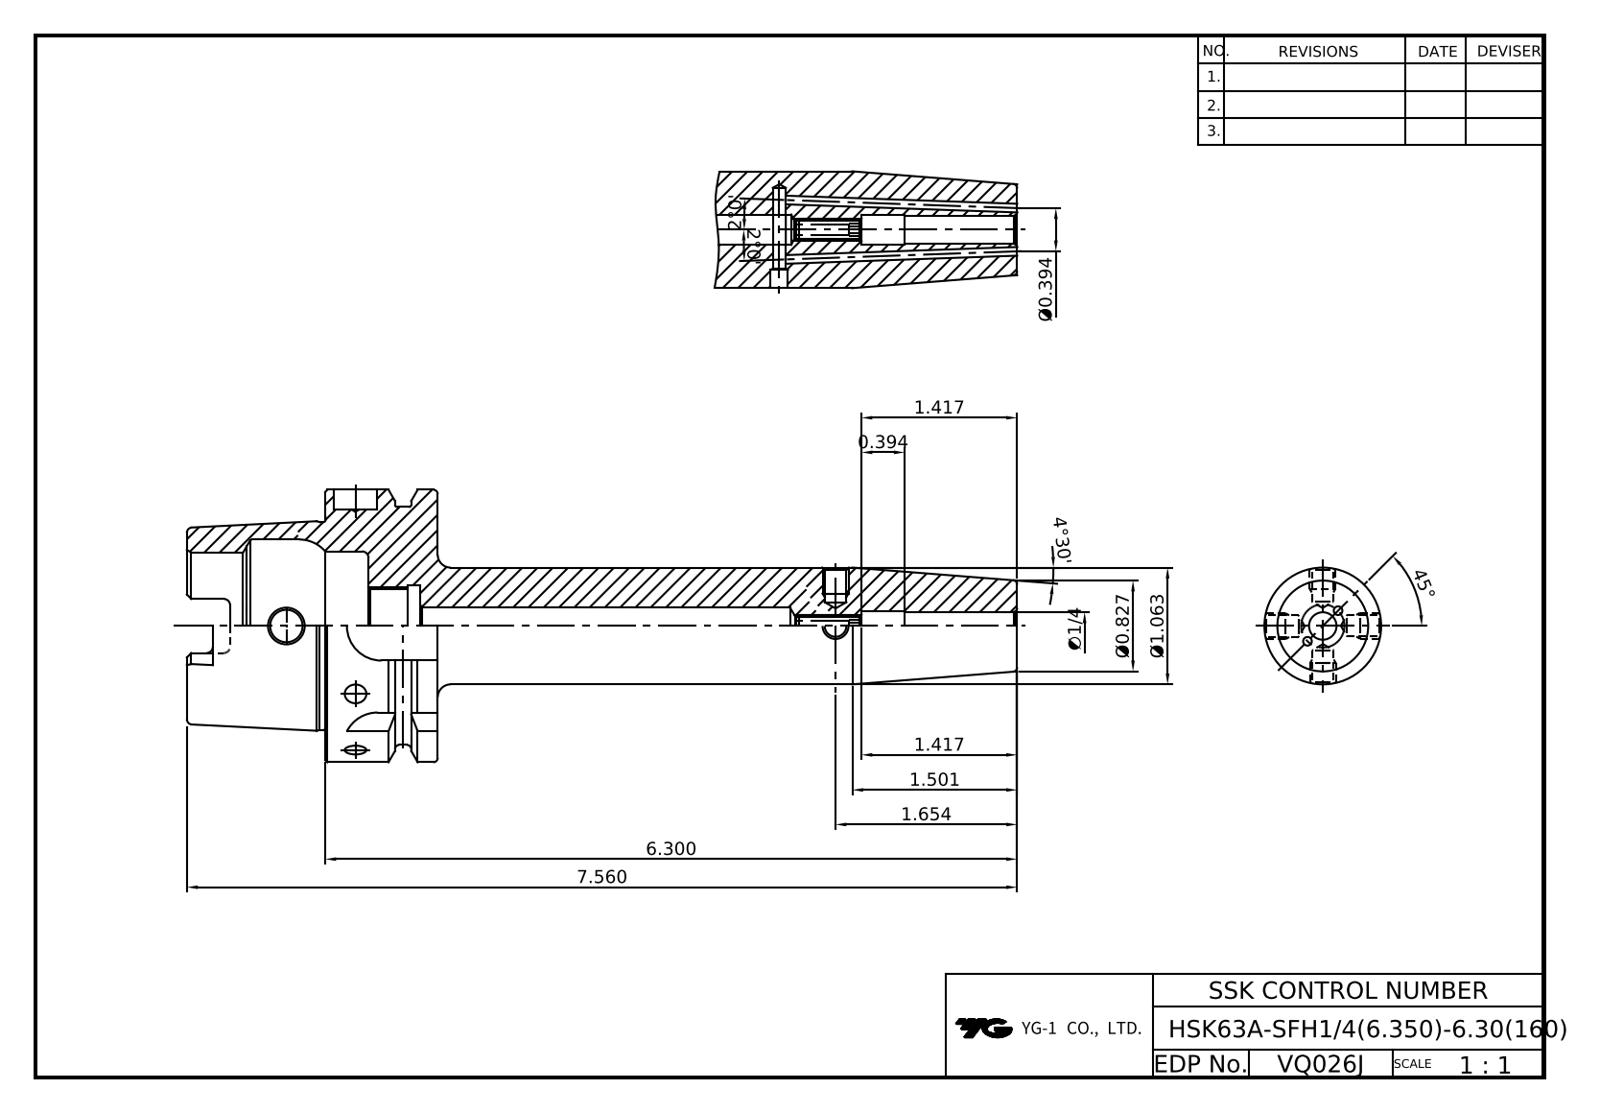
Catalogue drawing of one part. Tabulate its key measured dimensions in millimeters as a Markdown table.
| quantity | value |
| --- | --- |
| part name | VQ026J-HSK63A-SFH0_25-6_30 |
| STEP written by | CREO PARAMETRIC BY PTC INC, 2018100 (CONFIG_CONTROL_DESIGN) |
| units | millimeters |
| bodies | 1 solid, 208 faces (65 planar, 73 cylindrical, 70 other) |
| overall size | 192 × 63 × 63 |
| volume | 146 797 mm³ |
| surface area | 38 507 mm² |
| round holes (diameter × count) | 5 × 3, 2 × 2, 6 × 2, 4.2 × 1, 6.35 × 1, 6.75 × 1, 7.5 × 1, 8.4 × 1, 10 × 1, 17 × 1, 18 × 1, 19 × 1 |
| round bosses / shafts (diameter × count) | 63 × 1, 55 × 1, 48.04 × 1, 27 × 1 |
| partial cylindrical surfaces (radius × count) | 1.5 × 6, 2.88 × 4, 8 × 4 |
| main face-to-face distances | 26, 10, 16, 32, 6.12, 9.88, 42, 58, 4, 53 |
| hole center spacings | 111, 127 |
